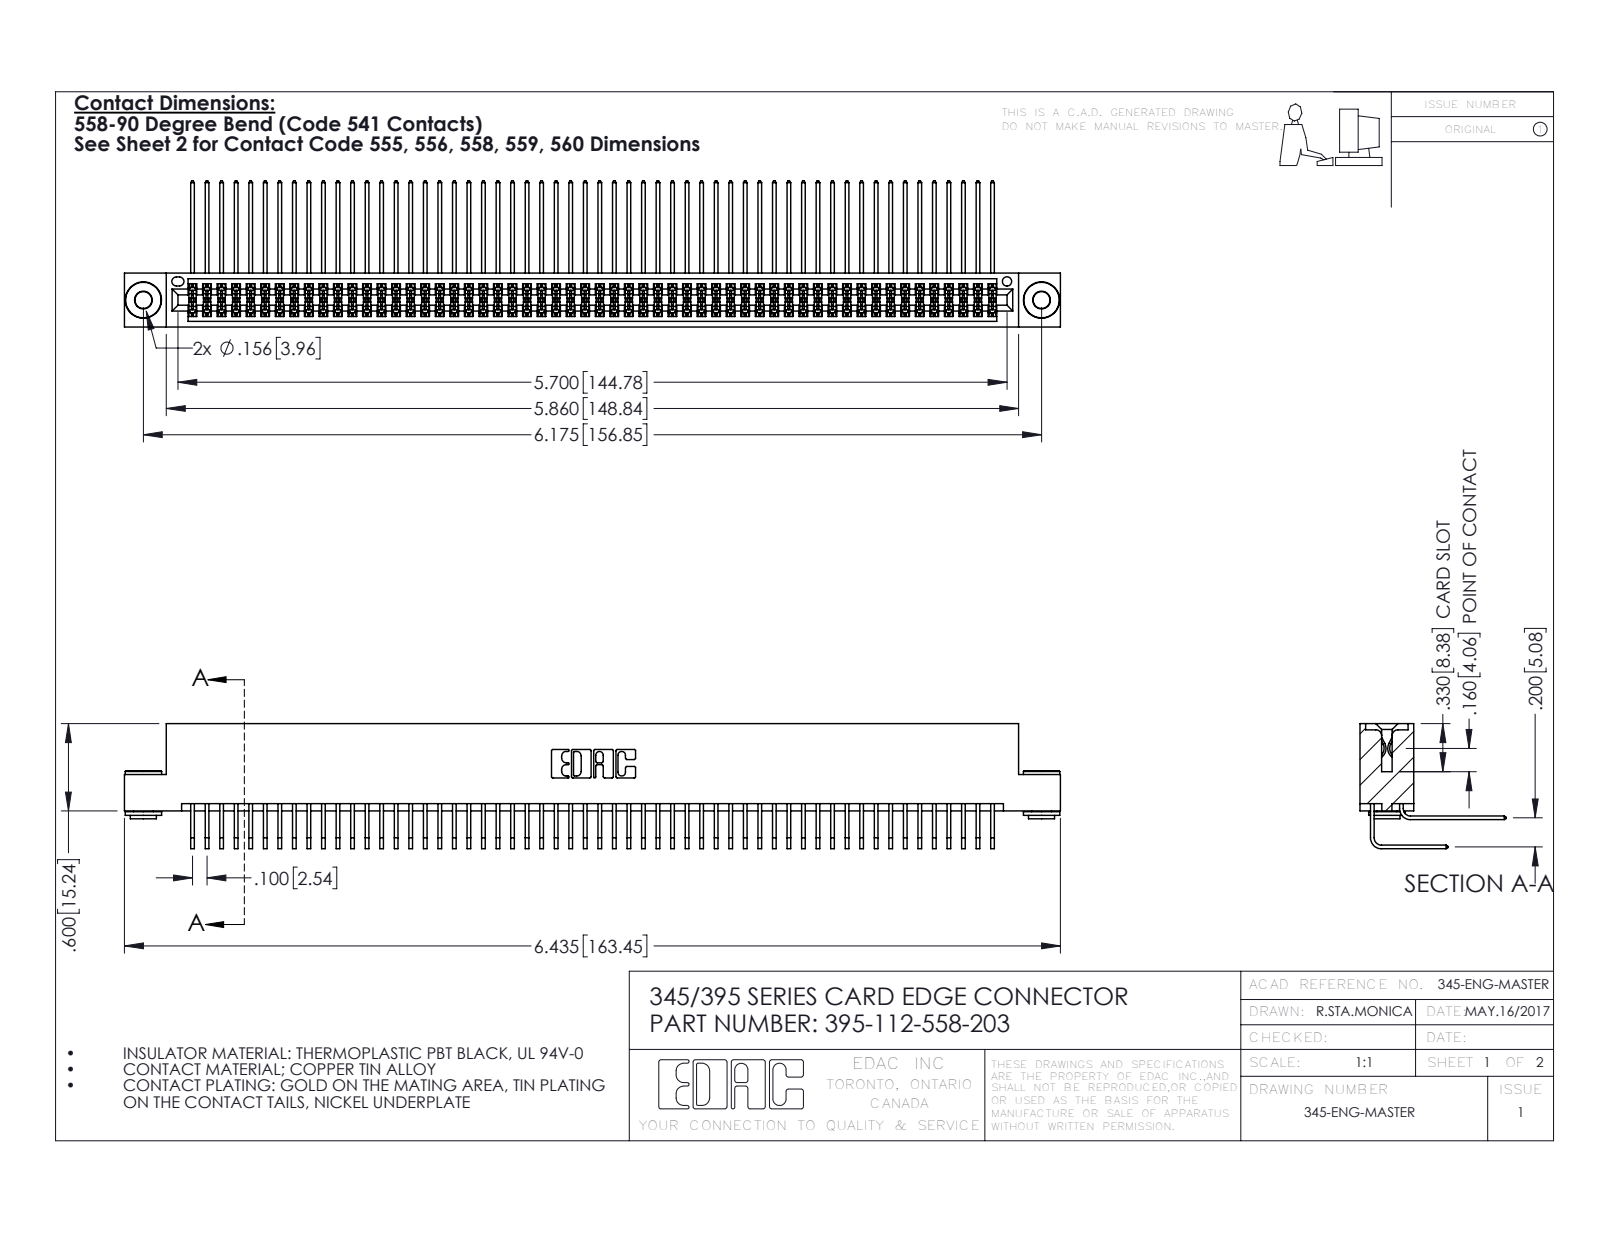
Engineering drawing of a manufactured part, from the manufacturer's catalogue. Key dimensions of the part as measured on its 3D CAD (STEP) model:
Part name (STEP PRODUCT): 395-112-558-203; 345-292-001_558 559 Tail - 1; 345-250-002_345-250-002-102; 345 Part_Flush Mounting Lugs - 0.156 Dia-TH (+1 more)
STEP written by: SolidWorks 2016 (CONFIG_CONTROL_DESIGN)
Units: inches
Bodies: 115 solids, 5988 faces (4010 planar, 1970 cylindrical, 8 other)
Overall size (bounding box): 6.435 × 1.005 × 0.859
Volume: 1.017 in³ · Surface area: 43.65 in²
Round holes (diameter × count): ⌀0.116 ×2, ⌀0.156 ×2, ⌀0.064 ×1
Round bosses / shafts (diameter × count): ⌀0.25 ×2, ⌀0.18 ×2, ⌀0.136 ×2
Partial cylindrical surfaces — rounded edges, fillets, slot ends (radius × count): R0.006 ×169, R0.01 ×22, R0.007 ×6, R0.031 ×6, R0.026 ×3, R0.014 ×2, R0.019 ×2, R0.022 ×2
Main face-to-face distances: 0.072, 0.298, 0.2, 0.37, 0.025, 0.098, 0.272, 0.225, 0.025, 0.175
Hole centre spacings: 0.27, 5.939, 6.175
